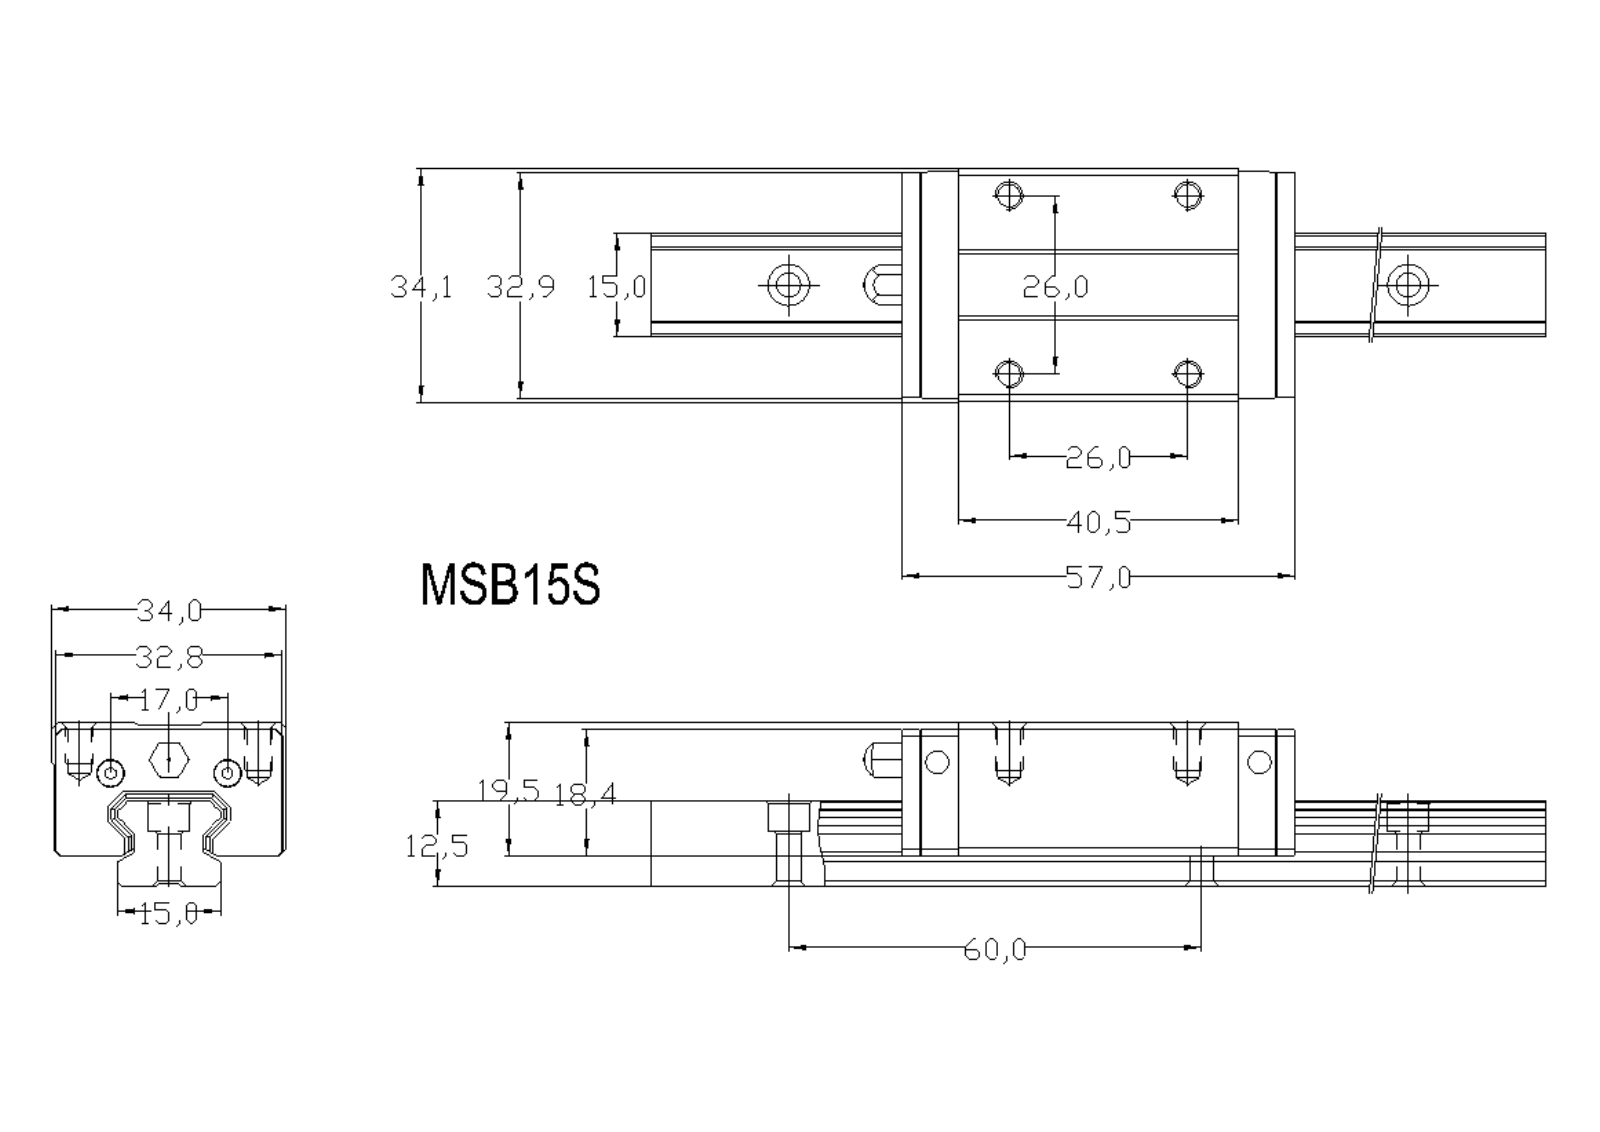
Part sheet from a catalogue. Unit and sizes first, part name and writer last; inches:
Units: inches
Overall size (bounding box): 6.299 × 1.339 × 0.945
Round holes (diameter × count): ⌀0.157 ×7, ⌀0.138 ×3, ⌀0.236 ×3
Partial cylindrical surfaces — rounded edges, fillets, slot ends (radius × count): R0.061 ×4, R0.039 ×2, R0.128 ×1
Main face-to-face distances: 0.492, 0.315, 0.177, 0.098, 0.453, 0.945, 0.768, 0.024, 0.472, 0.866
Hole centre spacings: 0.724, 1.024, 1.92, 2.919, 0.344, 1.448, 2.362, 0.669
Volume: 3.339 in³ · Surface area: 29.79 in²
Bodies: 3 solids, 151 faces (103 planar, 46 cylindrical, 2 other)
STEP written by: Kubotek KeyCreator V6.5.2 (0407) (CONFIG_CONTROL_DESIGN)
